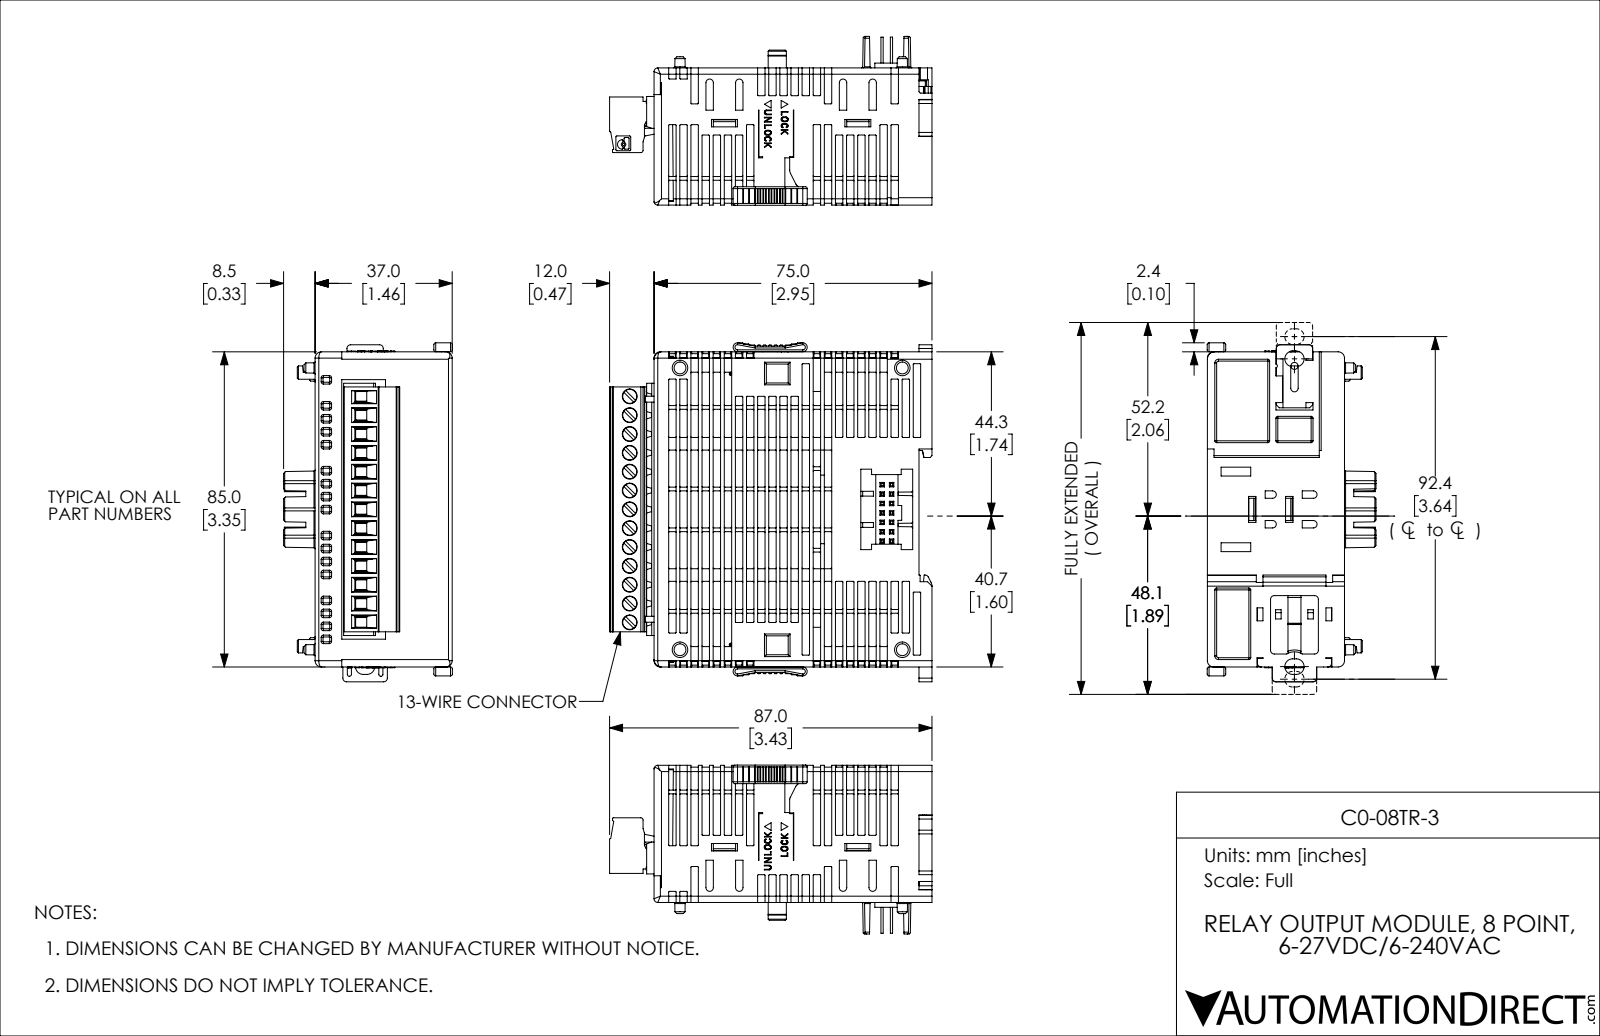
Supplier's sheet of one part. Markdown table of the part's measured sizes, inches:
| quantity | value |
| --- | --- |
| part name | C0-08TR-3 |
| STEP written by | SolidWorks 2019 (AUTOMOTIVE_DESIGN) |
| units | inches |
| bodies | 1 solid, 4458 faces (3231 planar, 1113 cylindrical, 114 other) |
| overall size | 3.6 × 3.425 × 1.793 |
| volume | 14.04 in³ |
| surface area | 64.84 in² |
| round holes (diameter × count) | 0.157 × 13, 0.126 × 4 |
| round bosses / shafts (diameter × count) | 0.149 × 13, 0.075 × 1, 0.024 × 1 |
| partial cylindrical surfaces (radius × count) | 0.008 × 654, 0.004 × 69, 0.012 × 56, 0.02 × 47, 0.039 × 26, 0.115 × 13, 0.008 × 10, 0.067 × 6 |
| main face-to-face distances | 1.457, 0.067, 1.39, 2.815, 3.346, 0.118, 0.06, 3.286, 0.079, 0.039 |
| hole center spacings | 0.2, 0.4, 0.6, 0.8, 1, 1.2, 1.4, 1.6 |
